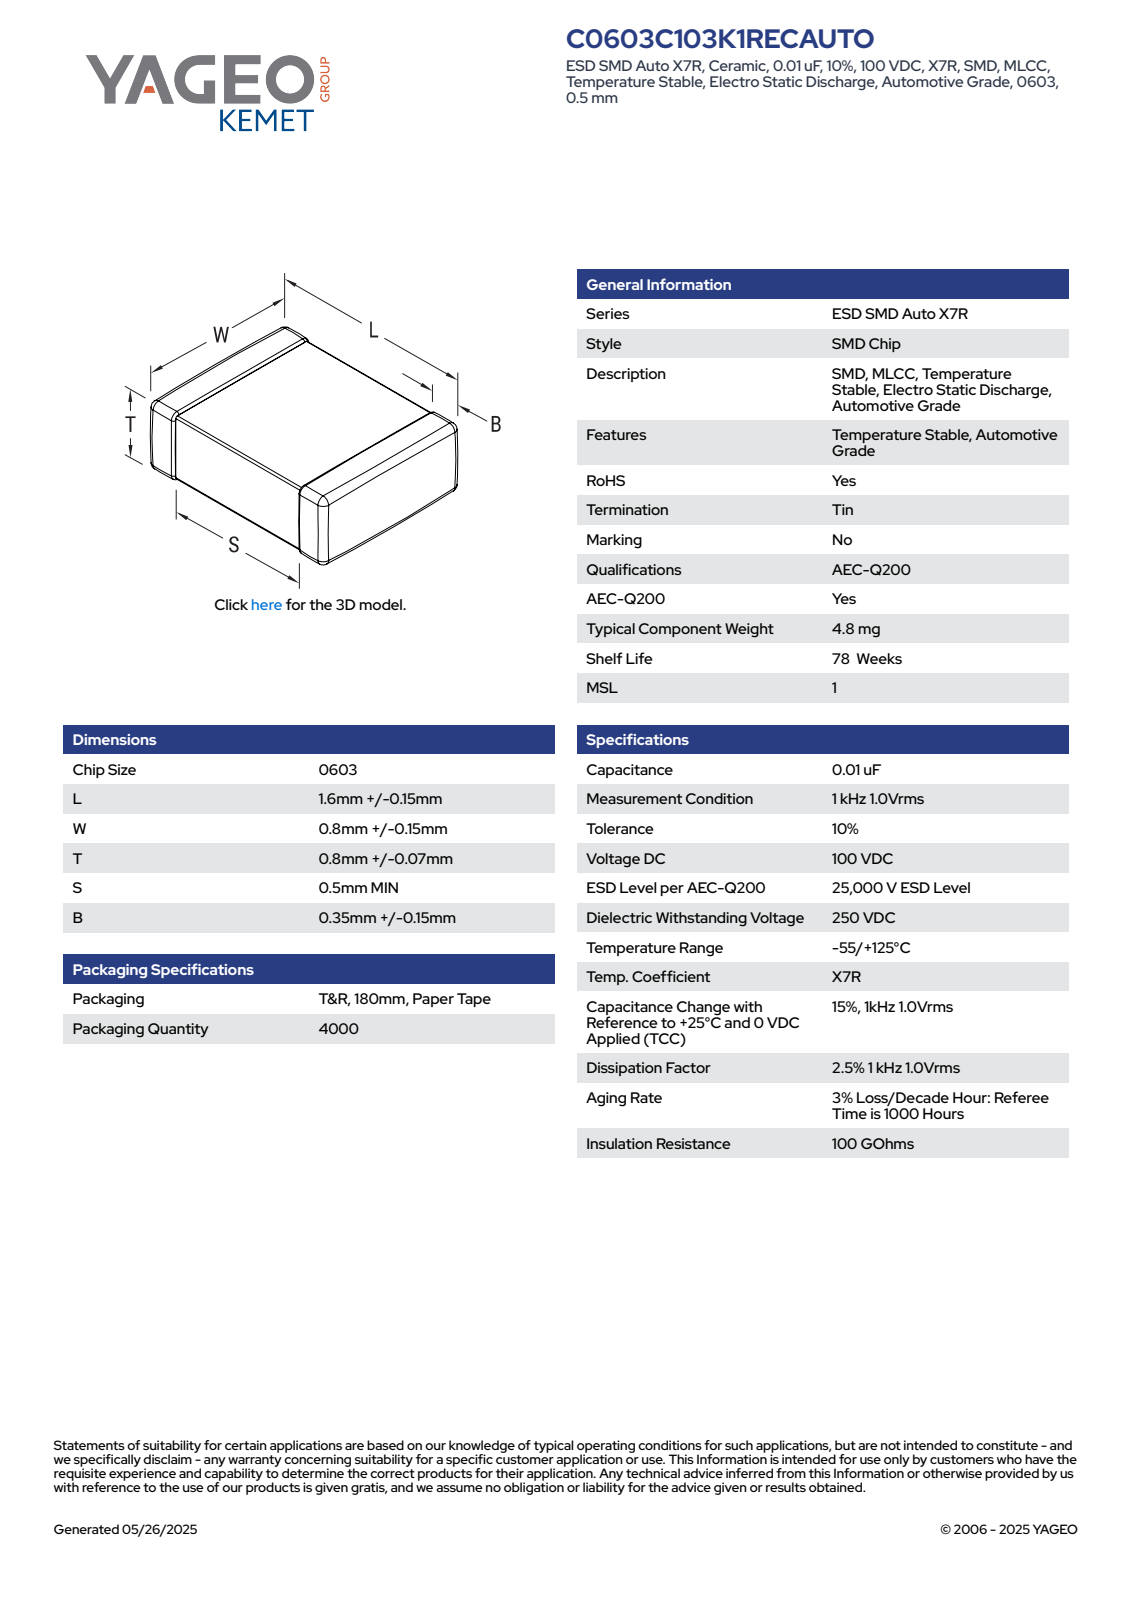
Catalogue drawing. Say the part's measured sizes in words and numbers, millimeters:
The part is named "CCS_CCSTD_0603_L1.75W0.95T0.87B0.35". Its 3-D file was written by "SolidWorks 2014 (AUTOMOTIVE_DESIGN)". It is 4 solids with 129 faces: 71 planar, 42 cylindrical and 16 other. Overall it measures 1.75 by 0.95 by 0.87 millimeters. Its volume is 1 cubic millimeters and its surface area 8 square millimeters. The main face-to-face distances are 0.85, 0.93, 0.83, 0.91, 1.75, 0.87, 0.95, 0.86, 0.84, 0.81.
